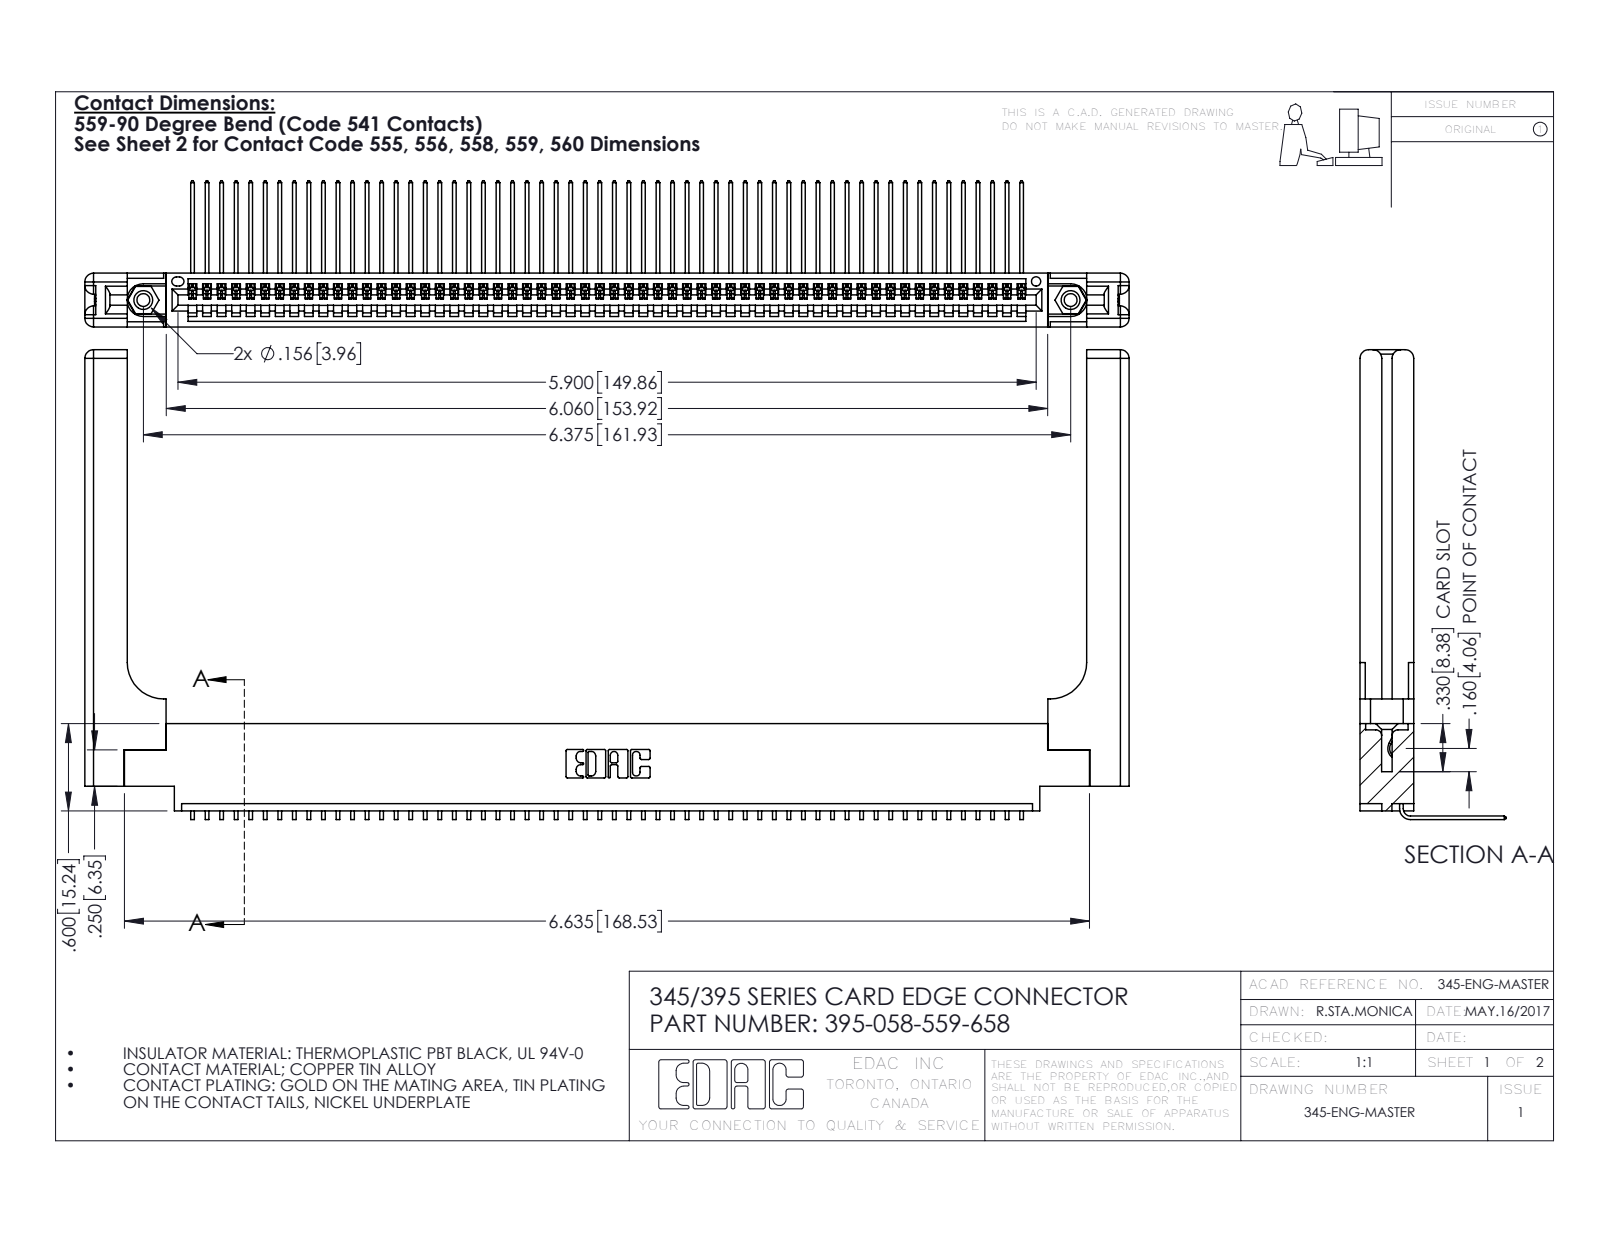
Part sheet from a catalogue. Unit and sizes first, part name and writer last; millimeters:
Units: millimetres
Overall size (bounding box): 182.3 × 82 × 25.5
Round holes (diameter × count): ⌀2.3 ×2, ⌀3.2 ×2, ⌀4 ×2, ⌀1.6 ×1
Round bosses / shafts (diameter × count): ⌀3.9 ×2
Partial cylindrical surfaces — rounded edges, fillets, slot ends (radius × count): R0.2 ×116, R0.3 ×22, R1.5 ×16, R0.2 ×6, R0.8 ×6, R0.7 ×3, R0.8 ×2, R0.8 ×2
Main face-to-face distances: 9.4, 1.8, 7.6, 2.5, 6.9, 0.6, 5.1, 5.7, 3.8, 3.8
Hole centre spacings: 6.9, 155.9, 161.9
Volume: 26 040 mm³ · Surface area: 30 080 mm²
Bodies: 63 solids, 3866 faces (2668 planar, 1138 cylindrical, 60 other)
Part name (STEP PRODUCT): 395-058-559-658; 345-250-001_345-250-001-102; 345 Part_0.170 Offset - 0.156 Dia-TH; 345-220-058_345-220-058 (+1 more)
STEP written by: SolidWorks 2016 (CONFIG_CONTROL_DESIGN)
